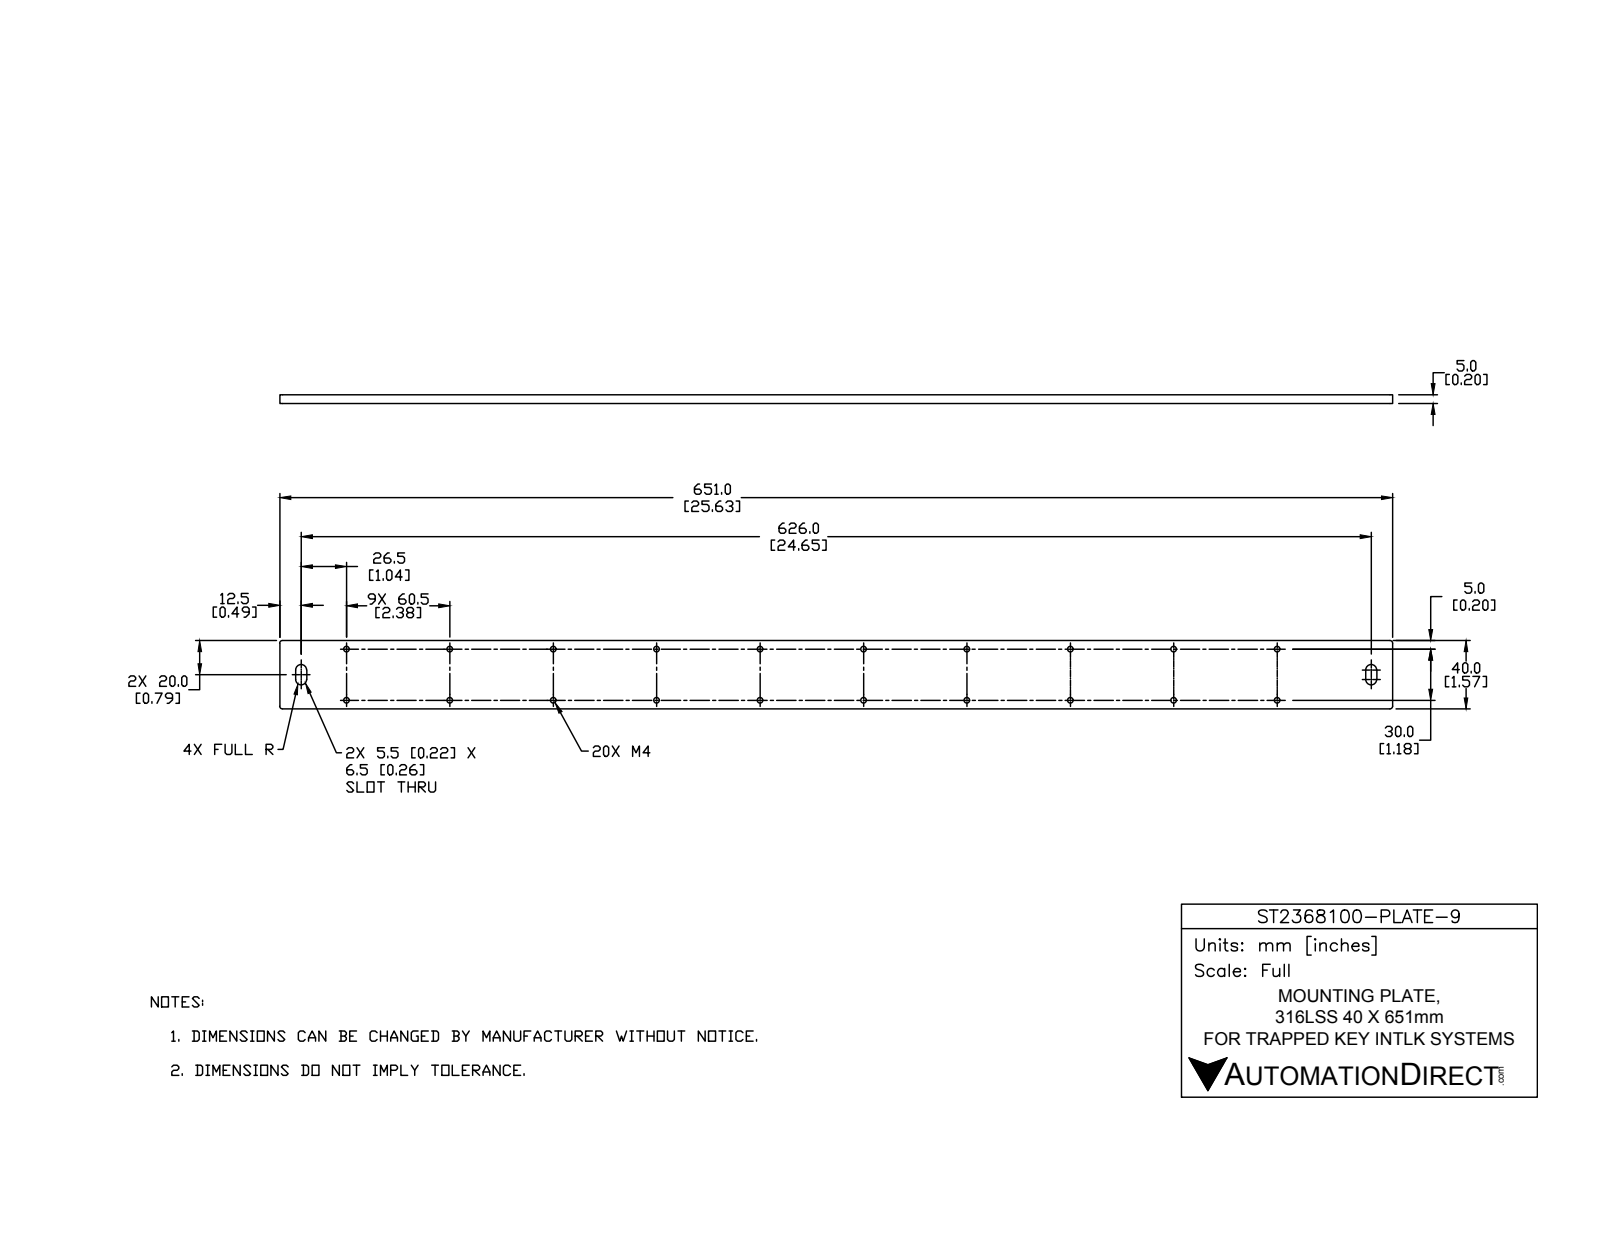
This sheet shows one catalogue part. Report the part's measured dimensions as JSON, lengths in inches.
{"part_name": "ST2368100-PLATE-9", "step_written_by": "SolidWorks 2017 (AUTOMOTIVE_DESIGN)", "units": "inches", "bodies": {"solids": 1, "faces": 70, "planar": 10, "cylindrical": 44, "other": 16}, "overall_size": [25.63, 1.575, 0.197], "volume_in3": 7.843, "surface_area_in2": 91.59, "round_holes": [[0.128, 20]], "partial_cylinders_radius": [[0.008, 8], [0.02, 8], [0.079, 4], [0.128, 4]], "face_to_face_distances": [0.197, 1.575, 25.63, 0.364, 0.62, 25.01, 25.266, 0.256, 24.646, 24.902], "hole_center_spacings": [2.362, 2.641, 4.724, 4.87, 7.087, 7.184, 9.449, 9.522]}
